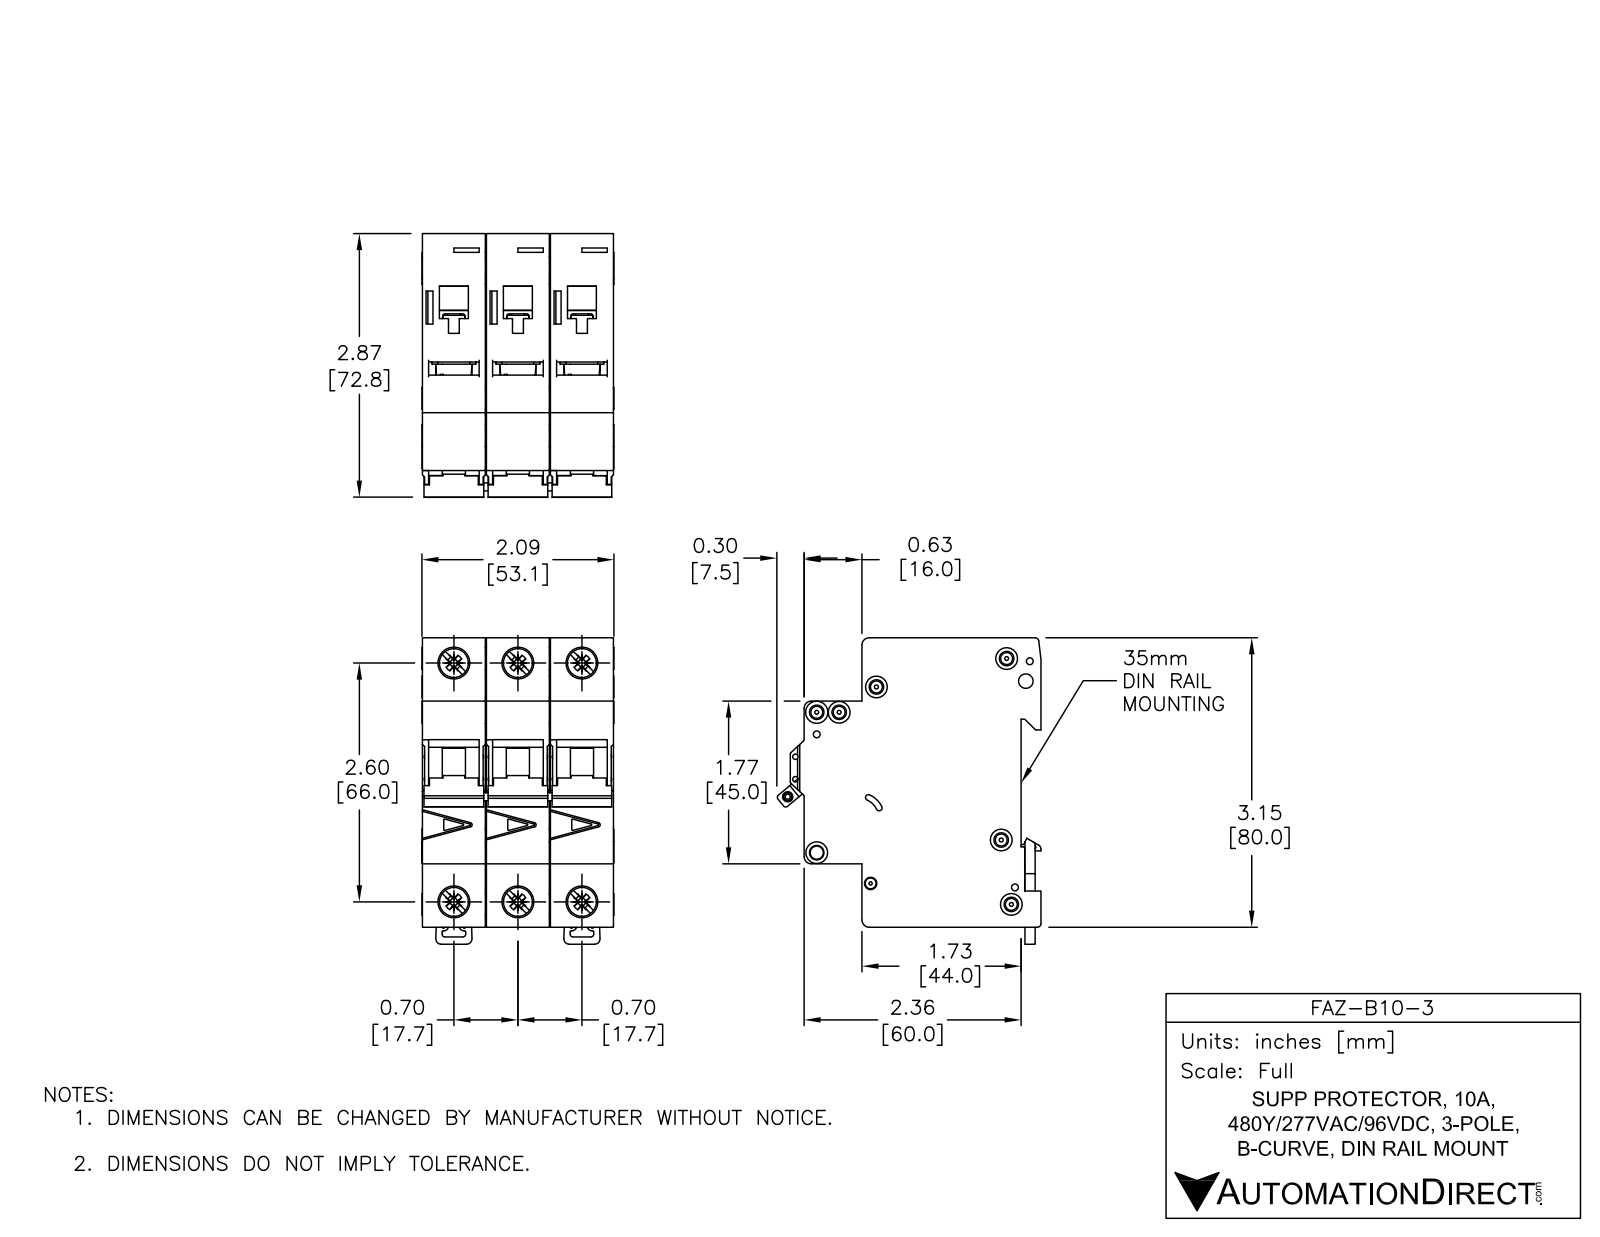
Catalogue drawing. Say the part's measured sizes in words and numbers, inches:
The part is named "FAZ-B10-3". Its 3-D file was written by "SolidWorks 2014 (AUTOMOTIVE_DESIGN)". It is 11 solids with 1650 faces: 697 planar, 590 cylindrical and 363 other. Overall it measures 3.338 by 2.876 by 2.091 inches. Its volume is 13.71 cubic inches and its surface area 89.98 square inches. Round holes: 6 of diameter 0.142, 4 of diameter 0.323, 3 of diameter 0.075, 2 of diameter 0.043, 2 of diameter 0.059, 2 of diameter 0.157, 2 of diameter 0.281, 1 of diameter 0.085, 1 of diameter 0.087, 1 of diameter 0.1, 1 of diameter 0.13, 1 of diameter 0.134. Round bosses or shafts: 4 of diameter 0.236, 3 of diameter 0.098, 2 of diameter 0.323. Partial cylindrical surfaces (rounded edges, fillets, slot ends): 68 of radius 0.01, 25 of radius 0.02, 12 of radius 0.039, 12 of radius 0.079, 11 of radius 0.008, 3 of radius 0.071, 2 of radius 0.031, 2 of radius 0.118. The main face-to-face distances are 0.697, 0.689, 1.394, 1.386, 2.083, 0.705, 3.129, 0.217, 1.949, 1.732. The hole center spacings are 0.697, 2.69, 2.598, 0.244, 0.537, 1.394, 2.948, 0.189.
